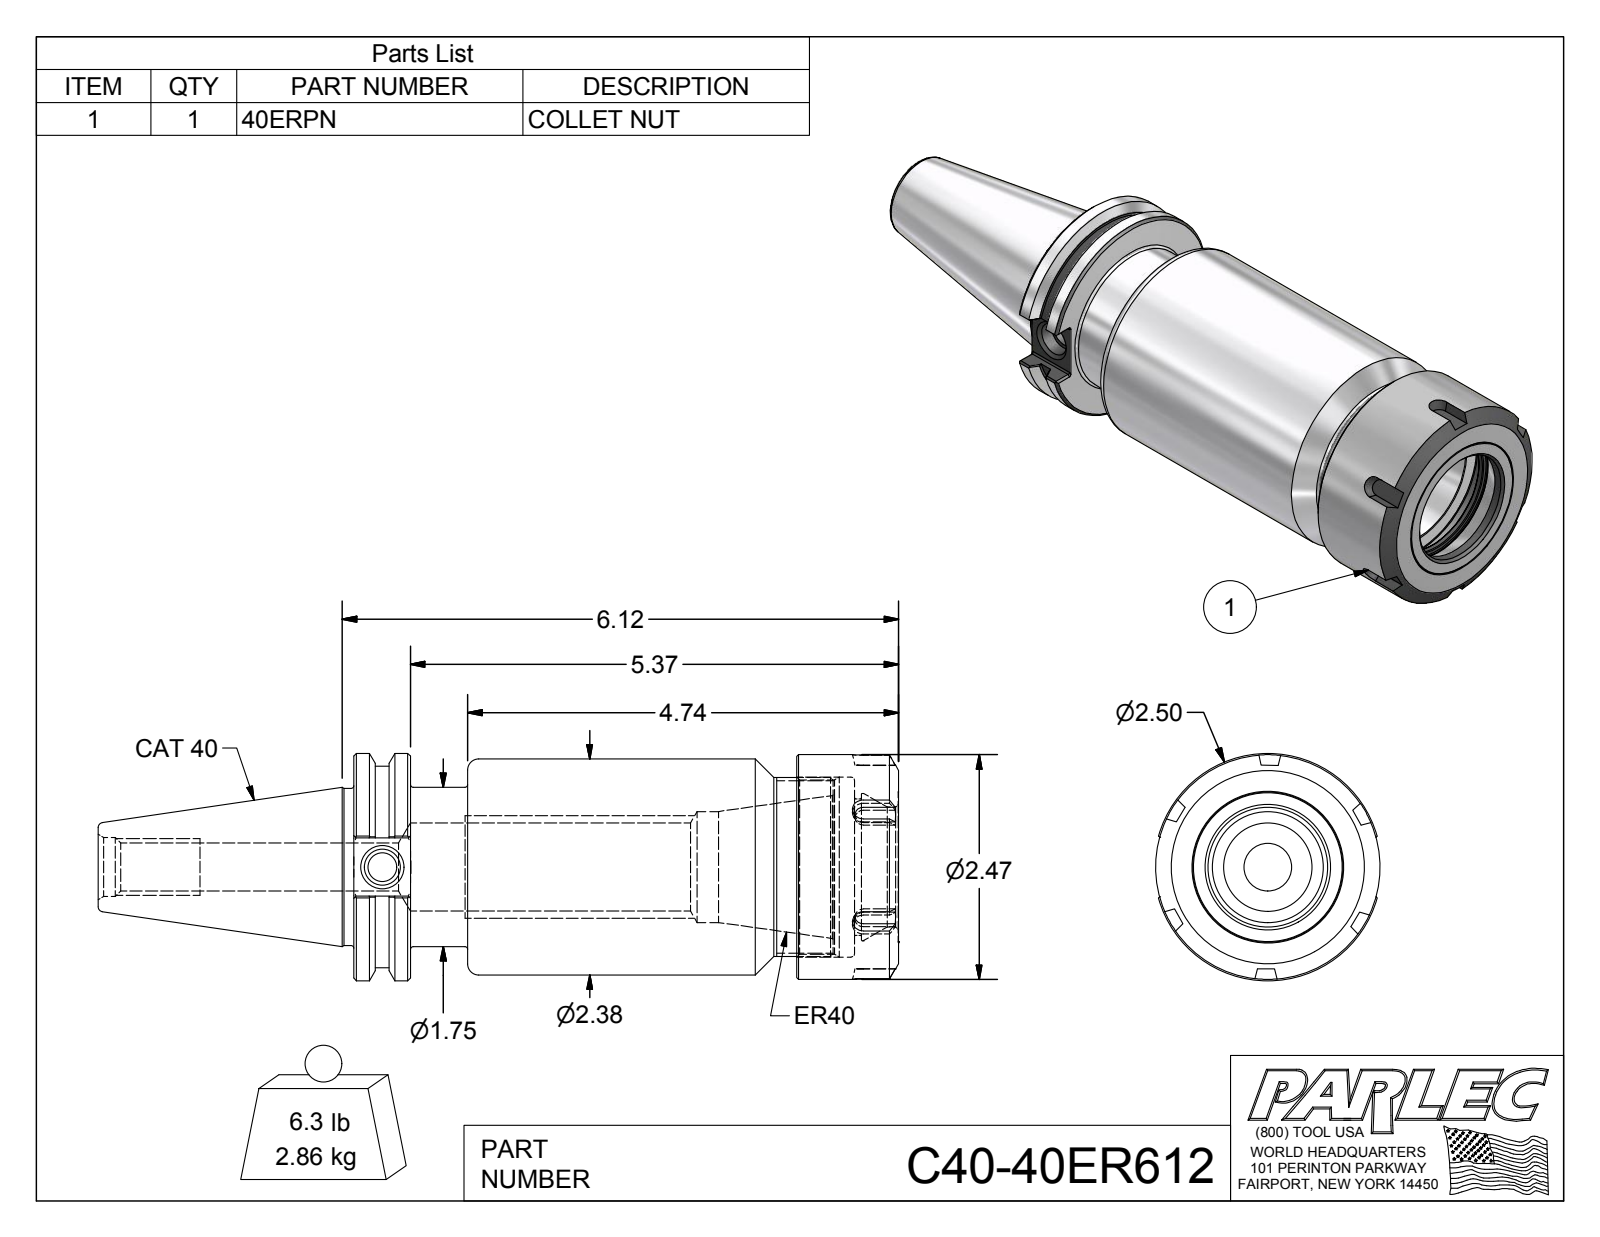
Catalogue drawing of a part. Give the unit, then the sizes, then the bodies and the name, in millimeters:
Units: millimetres
Overall size (bounding box): 223.7 × 63.5 × 62.7
Round holes (diameter × count): ⌀8 ×1, ⌀10.1 ×1, ⌀13.4 ×1, ⌀16.5 ×1, ⌀24.6 ×1, ⌀31 ×1, ⌀33.5 ×1, ⌀38.1 ×1, ⌀41.1 ×1, ⌀48.7 ×1, ⌀50.3 ×1
Round bosses / shafts (diameter × count): ⌀63.5 ×1, ⌀62.7 ×1, ⌀60.3 ×1, ⌀56.4 ×1, ⌀50 ×1, ⌀44.5 ×1, ⌀43.9 ×1
Partial cylindrical surfaces — rounded edges, fillets, slot ends (radius × count): R0.5 ×12
Main face-to-face distances: 152.3, 15.9, 136.4, 123.8, 108, 28.4, 140, 124.1, 16.2, 12.3
Volume: 366 300 mm³ · Surface area: 66 260 mm²
Bodies: 2 solids, 141 faces (55 planar, 34 cylindrical, 52 other)
Part name (STEP PRODUCT): C40-40ER612; C40-40ER6-1; 40ERPN
STEP written by: Autodesk Inventor 2012 (AUTOMOTIVE_DESIGN)
